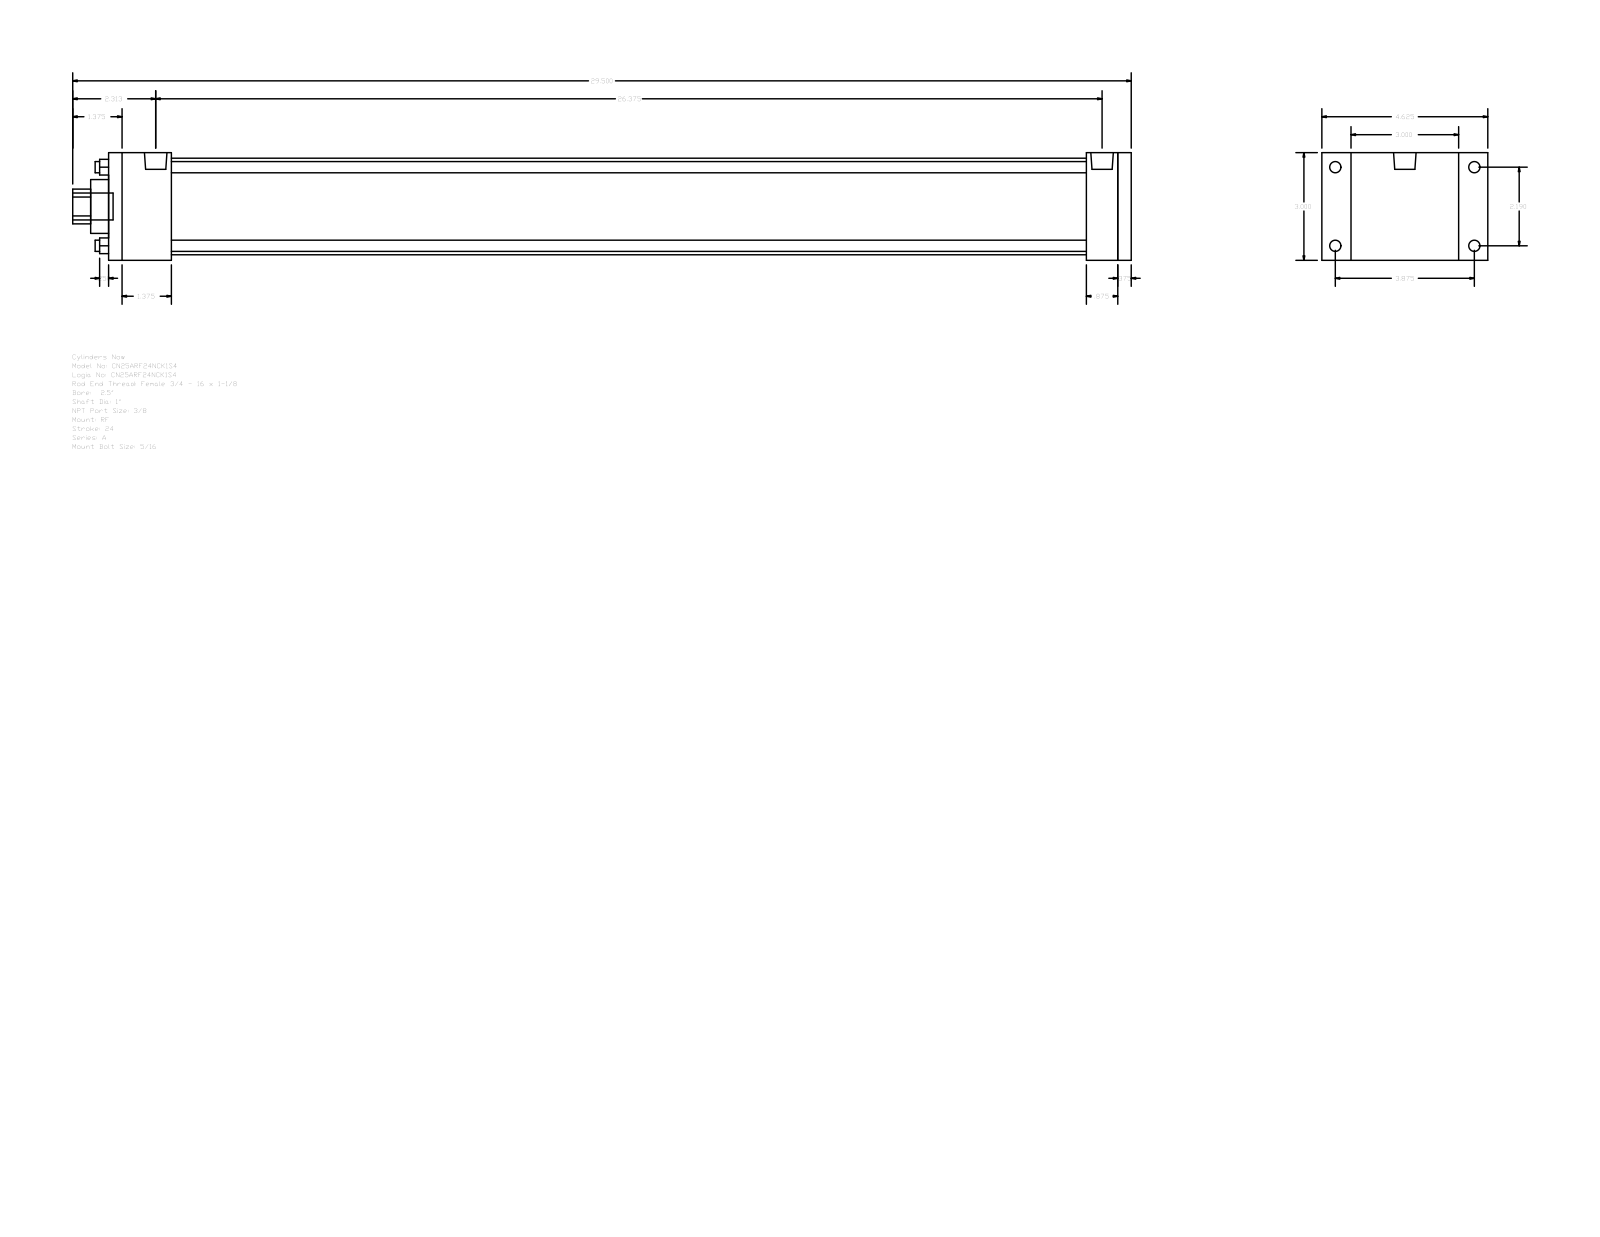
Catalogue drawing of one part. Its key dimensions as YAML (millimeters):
part_name: "A_RF__0250_1"
step_written_by: "GSSL Pune (CONFIG_CONTROL_DESIGN)"
units: millimeters
bodies: {solids: 0, faces: 92, planar: 64, cylindrical: 28, other: 0}
overall_size: [749.3, 117.47, 76.2]
round_holes:
  - {diameter: 7.94, count: 4}
  - {diameter: 25.4, count: 1}
  - {diameter: 38.1, count: 1}
  - {diameter: 68.33, count: 1}
round_bosses_or_shafts:
  - {diameter: 7.94, count: 4}
  - {diameter: 5.56, count: 4}
  - {diameter: 15.93, count: 2}
  - {diameter: 19.05, count: 1}
partial_cylinders:
  - {radius: 12.29, count: 1}
face_to_face_distances: [76.2, 723.9, 9.53, 714.37, 44.45, 692.15, 647.7, 669.92, 679.45, 22.22]
hole_center_spacings: [39.33, 55.62, 78.66]
